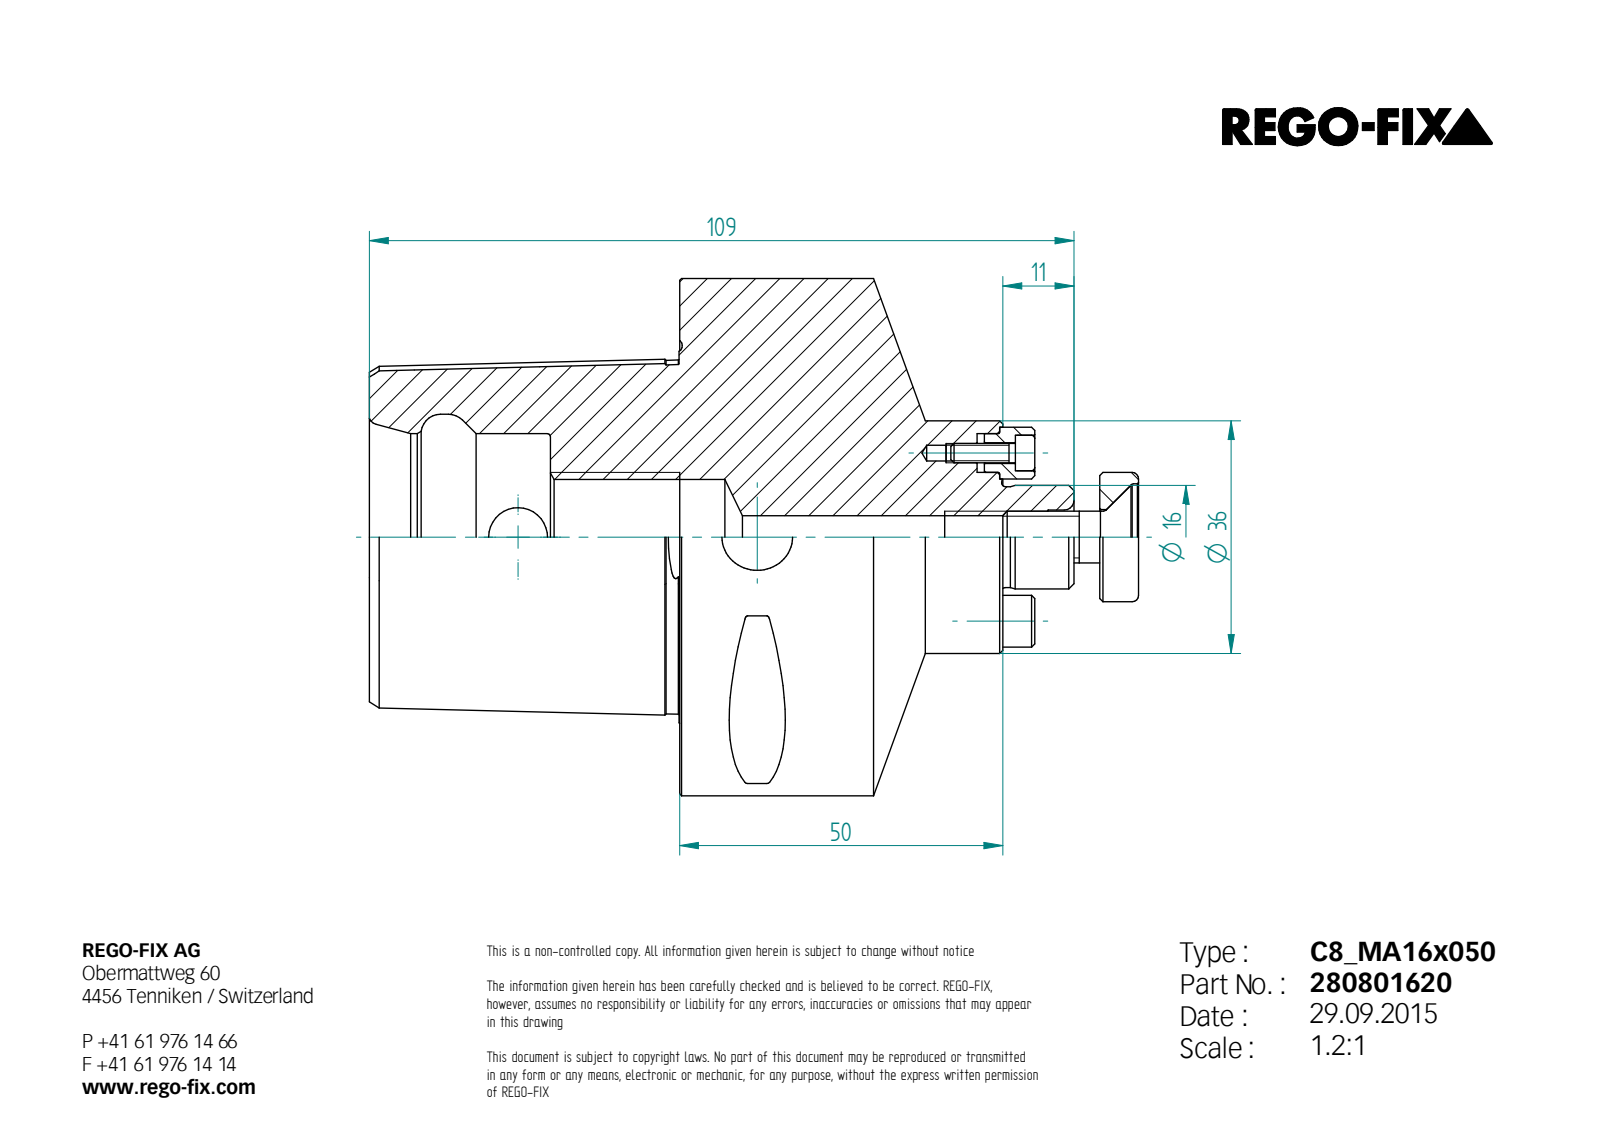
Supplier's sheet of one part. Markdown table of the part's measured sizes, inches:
| quantity | value |
| --- | --- |
| part name | 0003464; 0003381; 0007093; 0004885 (+1 more) |
| STEP written by | Unknown (AUTOMOTIVE_DESIGN) |
| units | inches |
| bodies | 7 solids, 229 faces (51 planar, 65 cylindrical, 113 other) |
| overall size | 4.685 × 3.15 × 3.15 |
| volume | 15.8 in³ |
| surface area | 57.71 in² |
| round holes (diameter × count) | 0.096 × 2, 0.097 × 2, 0.126 × 2, 0.236 × 2, 0.315 × 2, 0.157 × 1, 0.262 × 1, 0.331 × 1, 0.335 × 1, 0.358 × 1, 0.65 × 1, 0.702 × 1 |
| round bosses / shafts (diameter × count) | 0.217 × 2, 0.118 × 2, 3.15 × 1, 1.417 × 1, 0.787 × 1, 0.63 × 1, 0.614 × 1, 0.315 × 1 |
| partial cylindrical surfaces (radius × count) | 0.02 × 8, 0.236 × 1 |
| main face-to-face distances | 1.89, 0.787, 2.756, 3.858, 1.969, 1.281, 1.102, 1.886, 0.783, 1.972 |
| hole center spacings | 0.512, 1.024, 1.457 |
